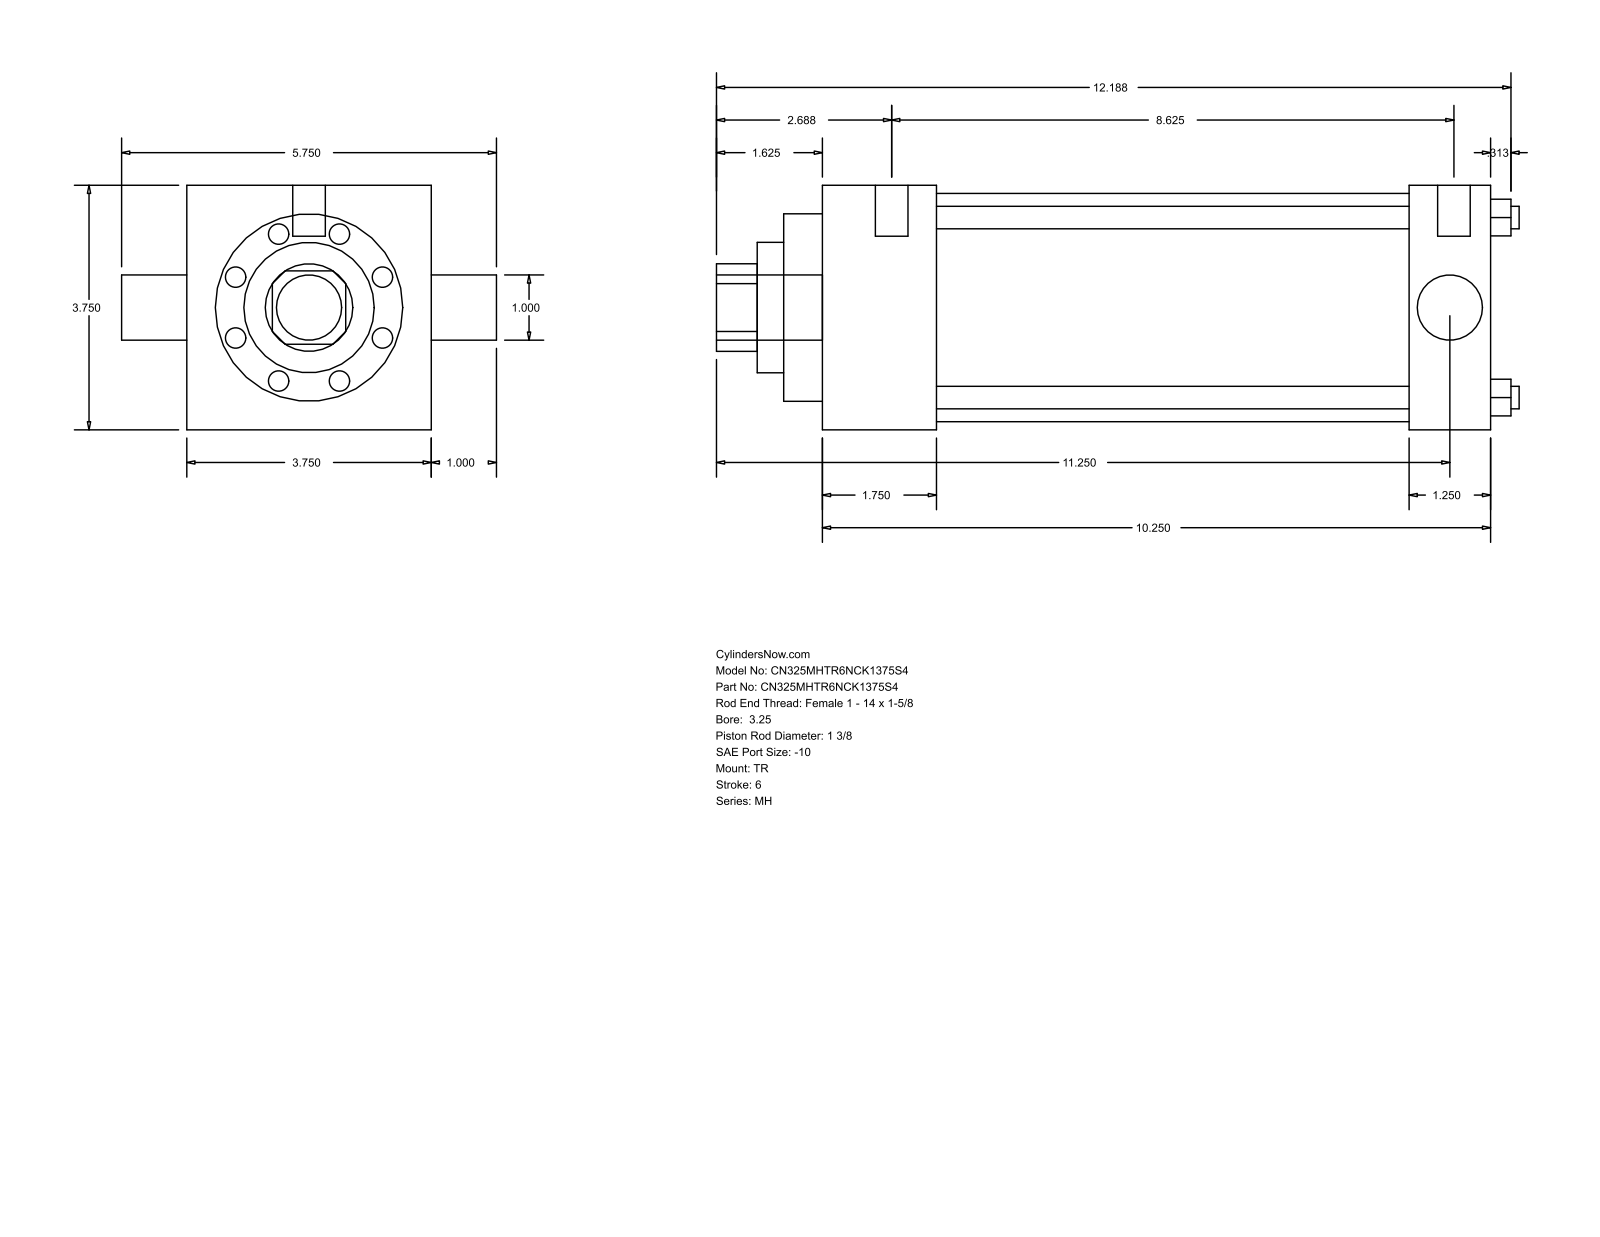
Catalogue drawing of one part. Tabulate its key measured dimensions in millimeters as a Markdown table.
| quantity | value |
| --- | --- |
| part name | MH_TR__0325_1.375 |
| STEP written by | GSSL Pune (CONFIG_CONTROL_DESIGN) |
| units | millimeters |
| bodies | 0 solids, 86 faces (61 planar, 25 cylindrical, 0 other) |
| overall size | 312.74 × 146.05 × 95.25 |
| round holes (diameter × count) | 8.76 × 4, 25.4 × 1, 34.92 × 1, 50.8 × 1, 73.03 × 1, 88.9 × 1 |
| round bosses / shafts (diameter × count) | 5.56 × 3, 12.7 × 2, 25.4 × 1 |
| partial cylindrical surfaces (radius × count) | 17.06 × 1 |
| main face-to-face distances | 95.24, 260.35, 44.45, 228.61, 184.16, 215.9, 31.74, 15.08, 59.53, 243.69 |
| hole center spacings | 49.57, 70.1, 99.14 |
